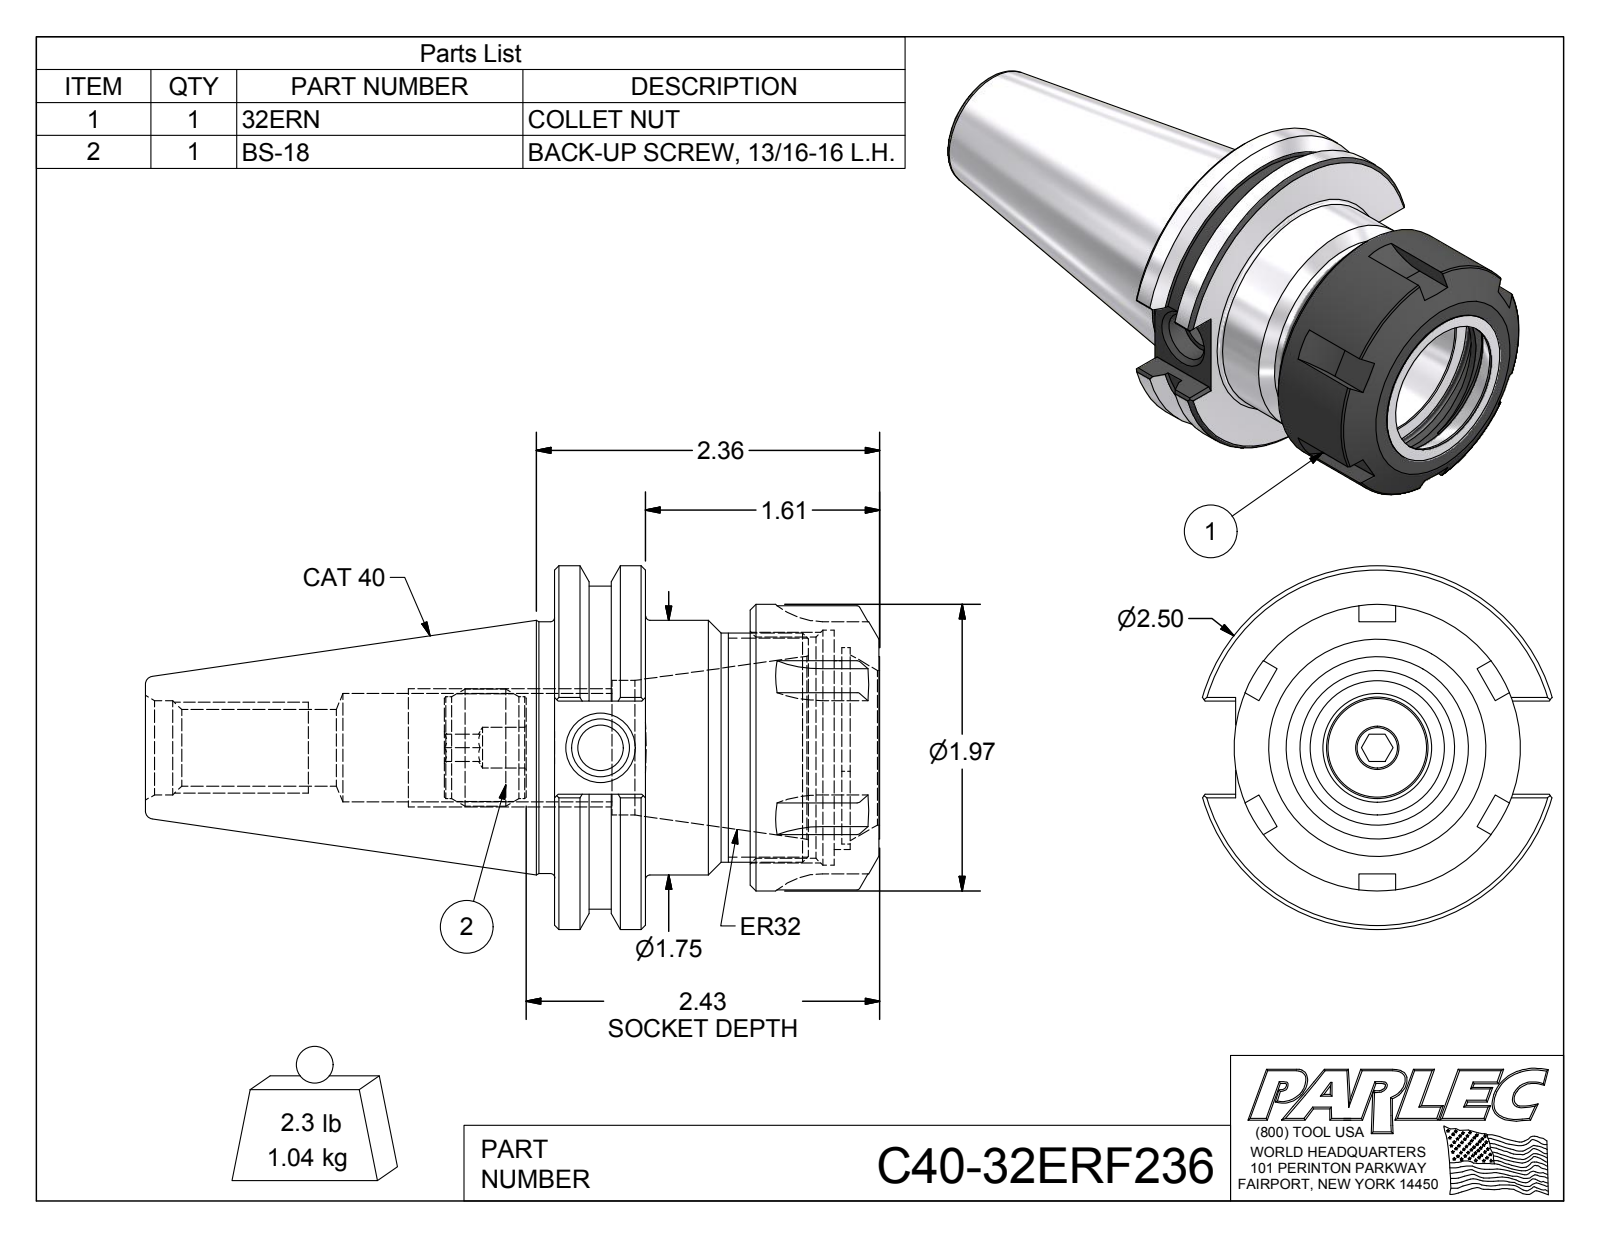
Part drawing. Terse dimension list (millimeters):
name: C40-32ER236-1; 32ERN; BS-18; C40-32ERF236
written by: Autodesk Inventor 2016 (AUTOMOTIVE_DESIGN)
unit: mm
bodies: 3 solids, 171 faces (75 planar, 38 cylindrical, 58 other)
size: 128.21 × 63.5 × 61.05
volume: 135 455 mm³; area: 37 355 mm²
holes: 1× ⌀7.11, 1× ⌀8, 1× ⌀10.05, 1× ⌀13.39, 1× ⌀16.46, 1× ⌀18.92, 1× ⌀23.5, 1× ⌀27, 1× ⌀33.02, 1× ⌀38.65, 1× ⌀41
bosses: 1× ⌀63.5, 1× ⌀56.36, 1× ⌀50, 1× ⌀44.45, 1× ⌀43.94, 1× ⌀40, 1× ⌀20.45, 1× ⌀17.78
rounds: 12× R0.51, 1× R14.9, 1× R17.5
face distances: 15.88, 56.77, 40.89, 34, 18.12, 22.77, 49, 33.12, 15, 7.77
hole spacings: 1.86
